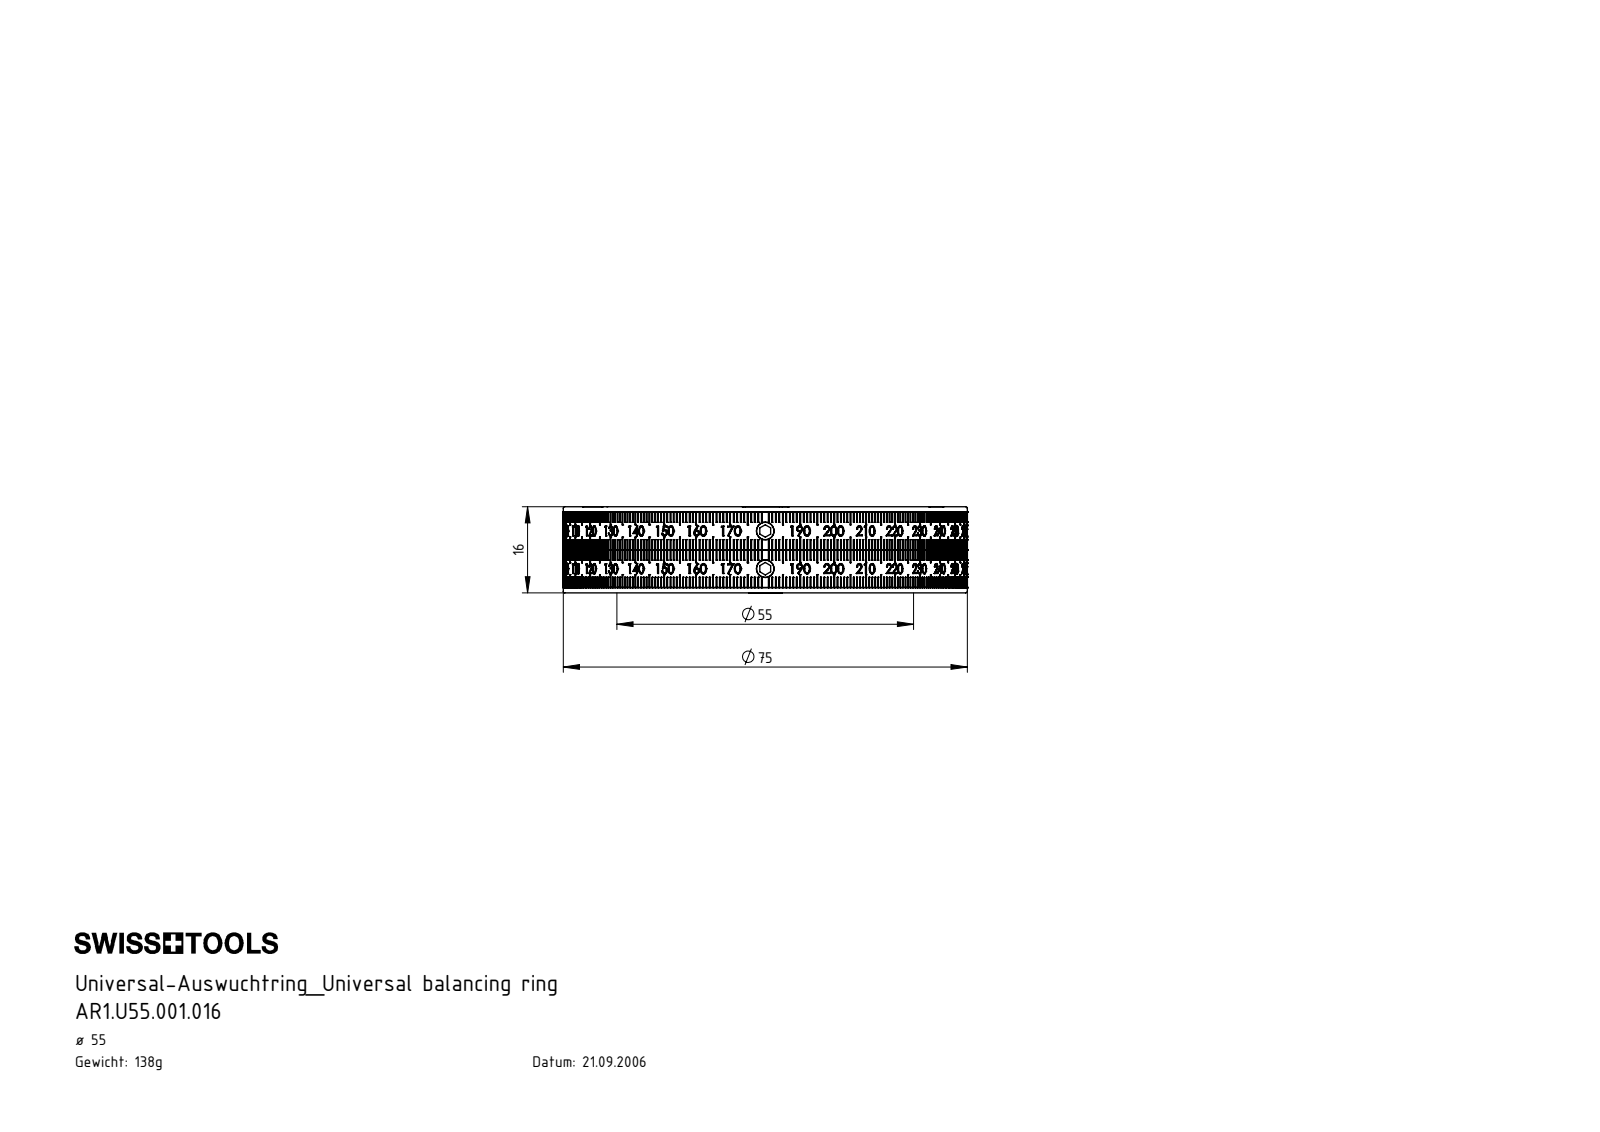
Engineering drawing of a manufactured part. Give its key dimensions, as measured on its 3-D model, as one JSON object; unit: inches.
{"part_name": "AR1.U55.001.016; ISO 4026 - M4 x 8; AR1-BG3.055.015_A_vereinfachte ansicht; AR1-BG1.055.007_B_vereinfachte ansicht (+1 more)", "step_written_by": "SolidWorks 2017 (AUTOMOTIVE_DESIGN)", "units": "inches", "bodies": {"solids": 6, "faces": 86, "planar": 45, "cylindrical": 27, "other": 14}, "overall_size": [2.953, 2.953, 0.63], "volume_in3": 1.378, "surface_area_in2": 46.42, "round_holes": [[0.13, 2], [2.167, 1], [2.224, 1], [2.283, 1]], "round_bosses_or_shafts": [[0.157, 2], [2.953, 1]], "partial_cylinders_radius": [[0.118, 2], [1.437, 1]], "face_to_face_distances": [0.276, 0.039, 0.591, 0.122, 0.154, 0.272, 0.118, 0.15, 0.551, 0.63], "hole_center_spacings": [0.276]}
